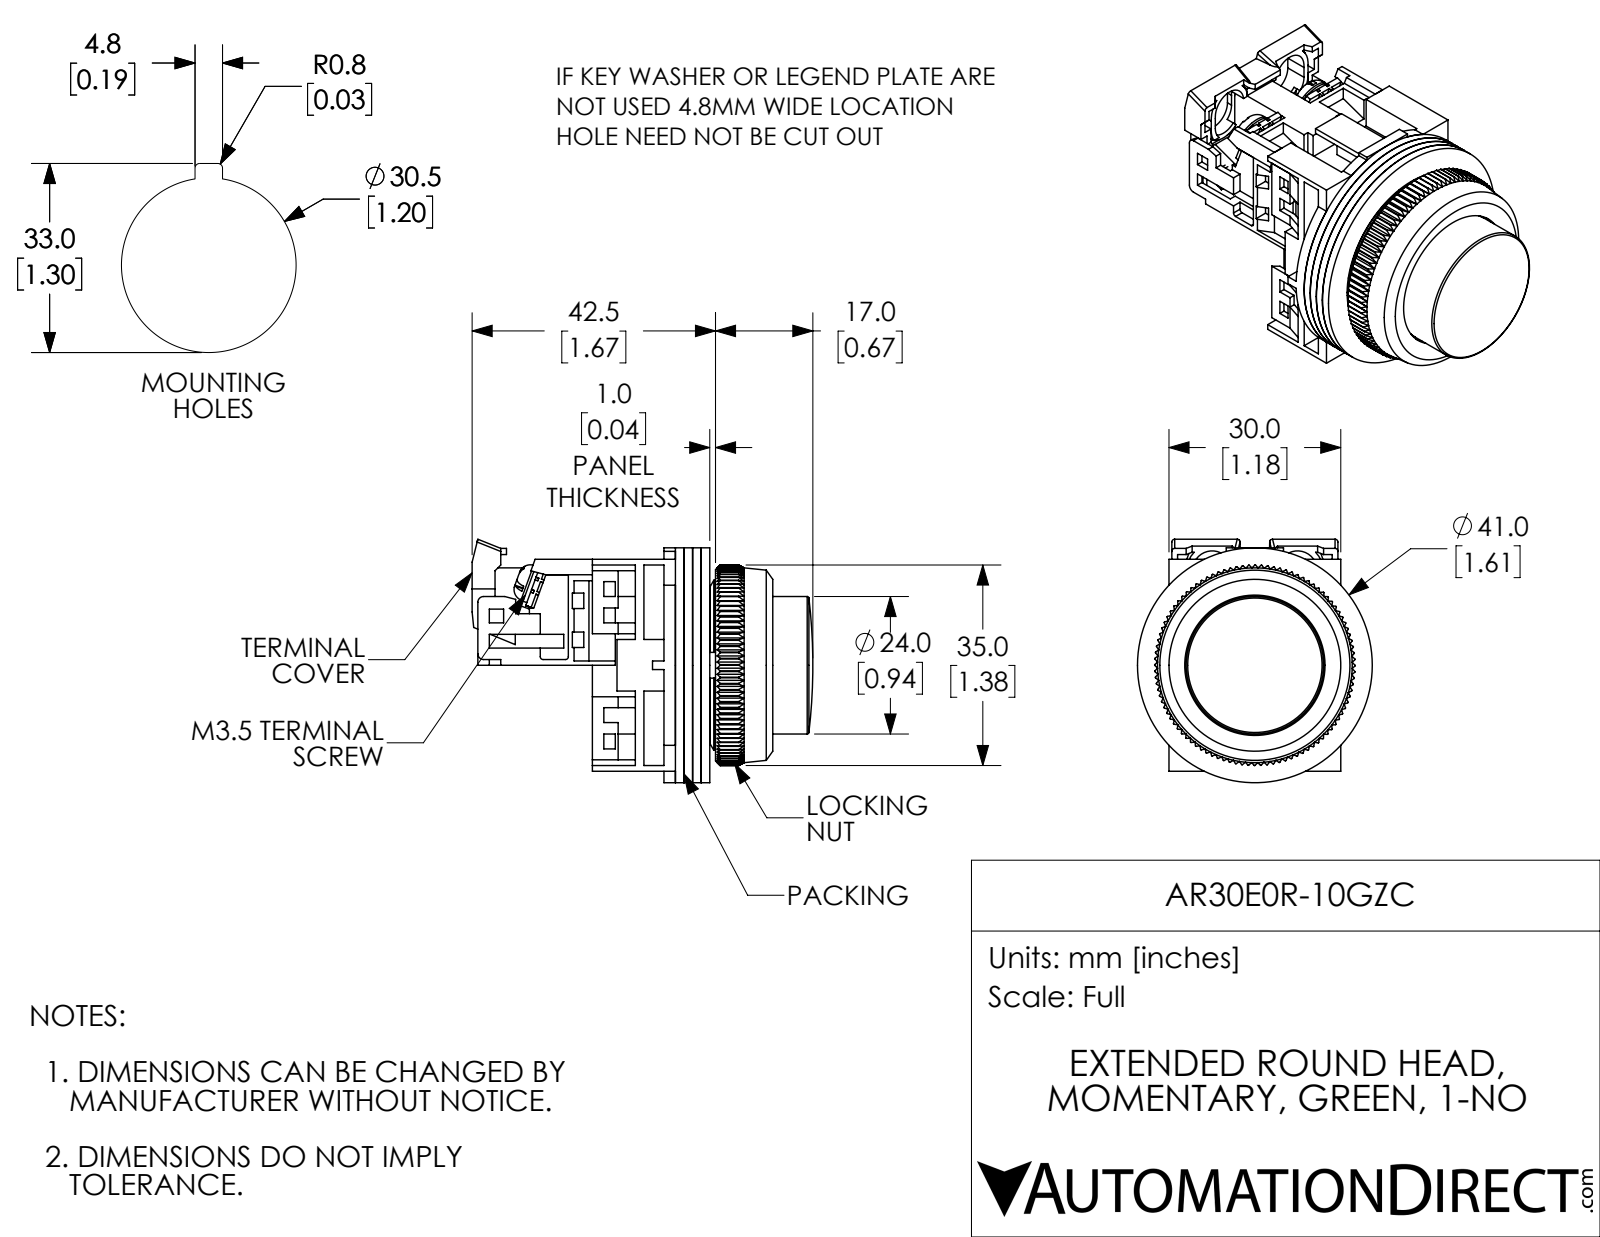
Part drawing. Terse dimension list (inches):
name: AR30E0R-10GZC
written by: SolidWorks 2017 (AUTOMOTIVE_DESIGN)
unit: in
bodies: 16 solids, 1234 faces (775 planar, 249 cylindrical, 210 other)
size: 2.342 × 1.673 × 1.614
volume: 1.642 in³; area: 48.85 in²
holes: 4× ⌀0.138, 2× ⌀0.142, 1× ⌀0.118, 1× ⌀0.472, 1× ⌀0.709, 1× ⌀0.787, 1× ⌀0.945, 1× ⌀0.965, 1× ⌀1.122, 1× ⌀1.252
bosses: 2× ⌀0.26, 2× ⌀0.138, 1× ⌀1.614, 1× ⌀1.181, 1× ⌀0.866, 1× ⌀0.551
rounds: 8× R0.059, 6× R0.02, 2× R0.039, 2× R0.138, 2× R0.177, 1× R0.118, 1× R0.398, 1× R0.449
face distances: 0.059, 0.118, 0.177, 0.039, 0.197, 0.079, 0.276, 0.689, 0.728, 0.602
hole spacings: 0.579, 0.61
